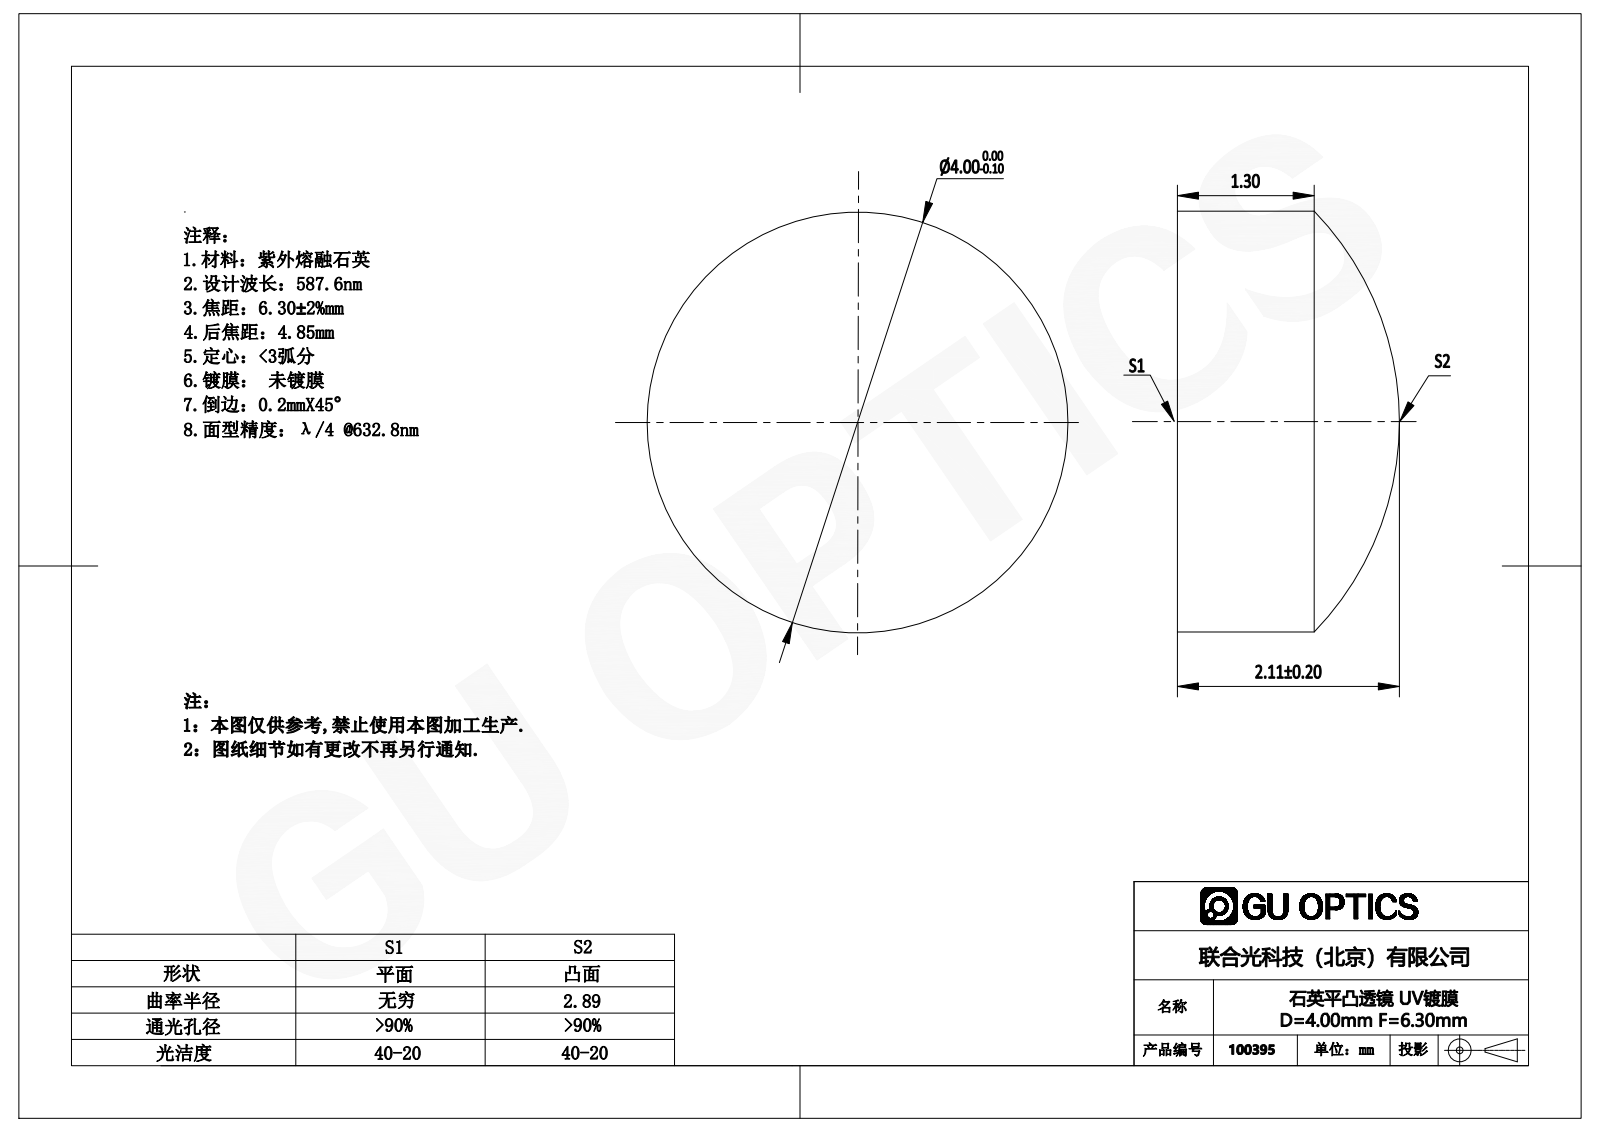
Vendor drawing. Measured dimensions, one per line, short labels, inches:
name: 100345
written by: SolidWorks 2016 (AUTOMOTIVE_DESIGN)
unit: in
bodies: 1 solid, 5 faces (1 planar, 2 cylindrical, 2 other)
size: 0.157 × 0.157 × 0.083
volume: 0.001 in³; area: 0.068 in²
bosses: 1× ⌀0.157
